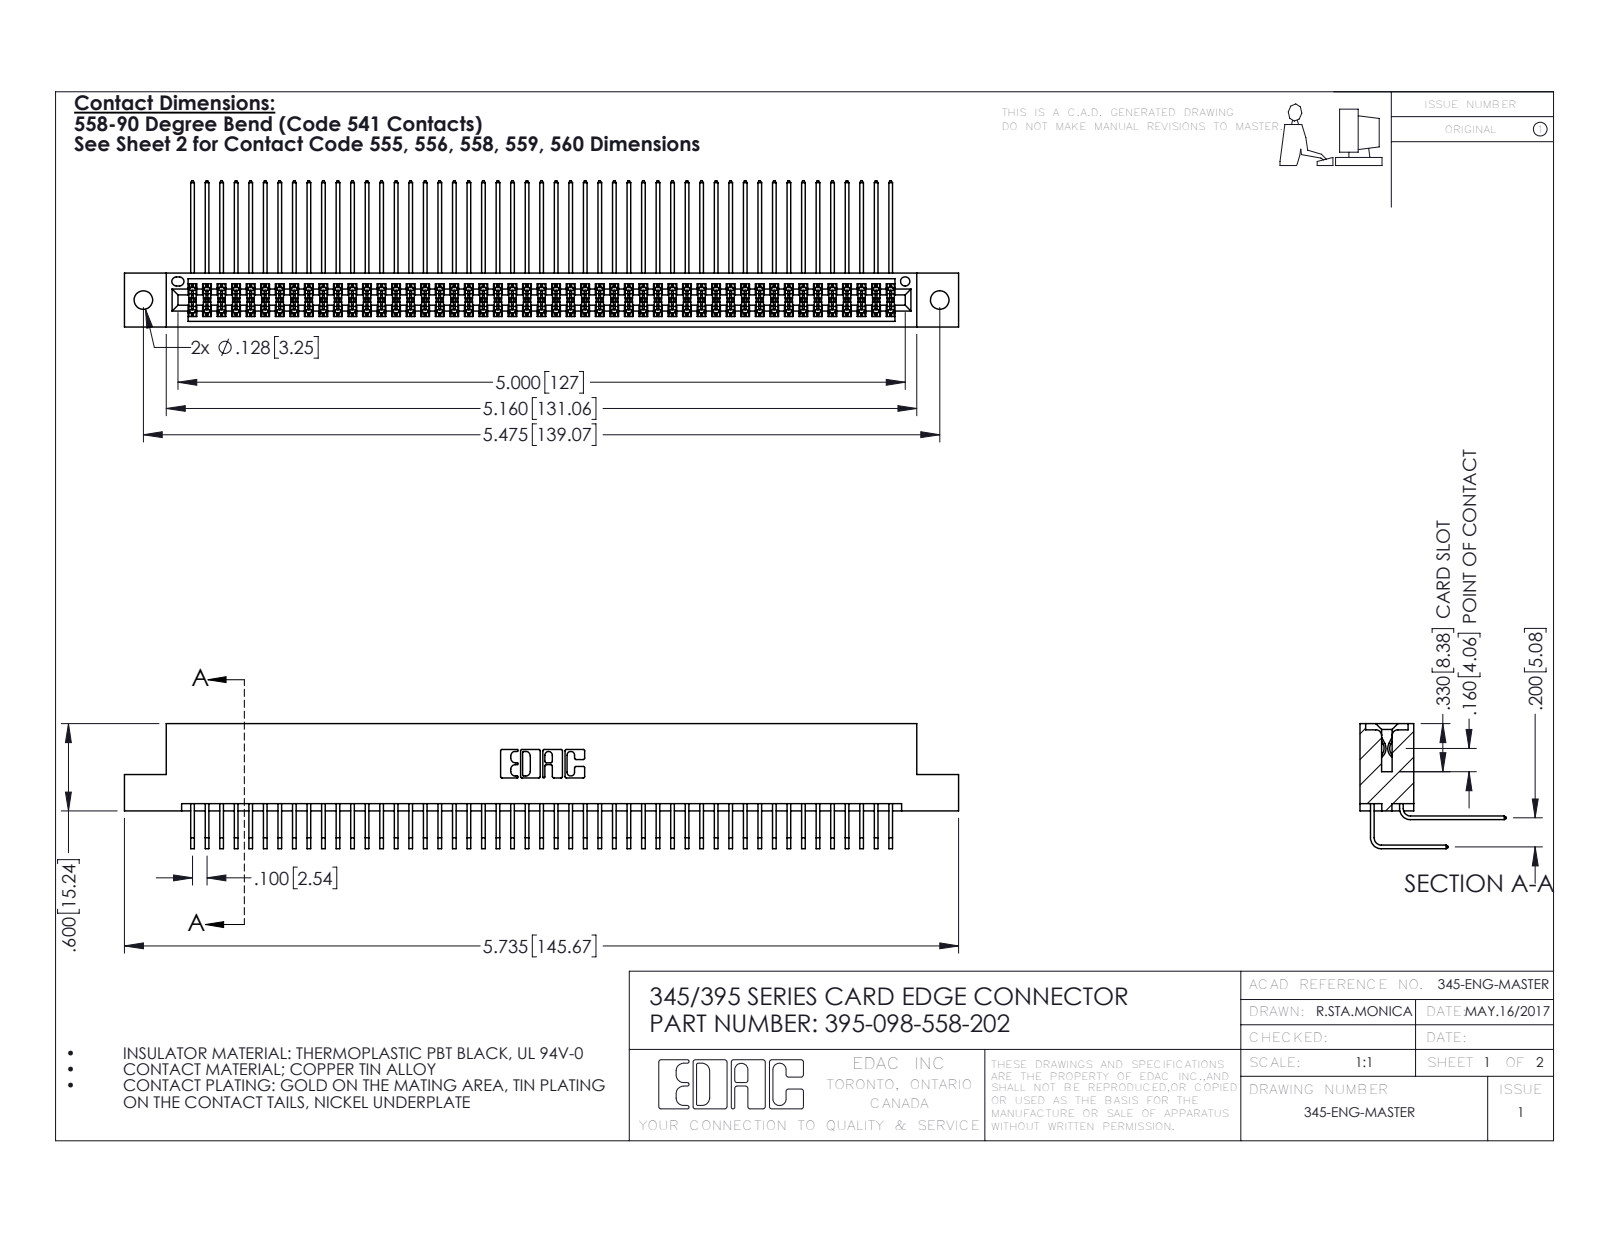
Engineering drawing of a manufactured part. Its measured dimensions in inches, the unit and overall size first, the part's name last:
Units: inches
Overall size (bounding box): 5.735 × 1.005 × 0.859
Round holes (diameter × count): ⌀0.128 ×2, ⌀0.064 ×1
Partial cylindrical surfaces — rounded edges, fillets, slot ends (radius × count): R0.006 ×148, R0.01 ×22, R0.007 ×6, R0.031 ×6, R0.026 ×3, R0.014 ×2, R0.019 ×2, R0.022 ×2
Main face-to-face distances: 0.072, 0.298, 0.2, 0.37, 0.098, 0.272, 0.025, 0.225, 0.025, 0.175
Hole centre spacings: 0.27, 5.239, 5.475
Volume: 0.9 in³ · Surface area: 37.69 in²
Bodies: 99 solids, 5222 faces (3510 planar, 1712 cylindrical, 0 other)
Part name (STEP PRODUCT): 345-292-001_558 559 Tail - 1; 395-098-558-202; 345 Part_Flush Mounting Lugs - 0.128 Dia; 345-292-001_558 Tail - 2
STEP written by: SolidWorks 2016 (CONFIG_CONTROL_DESIGN)
